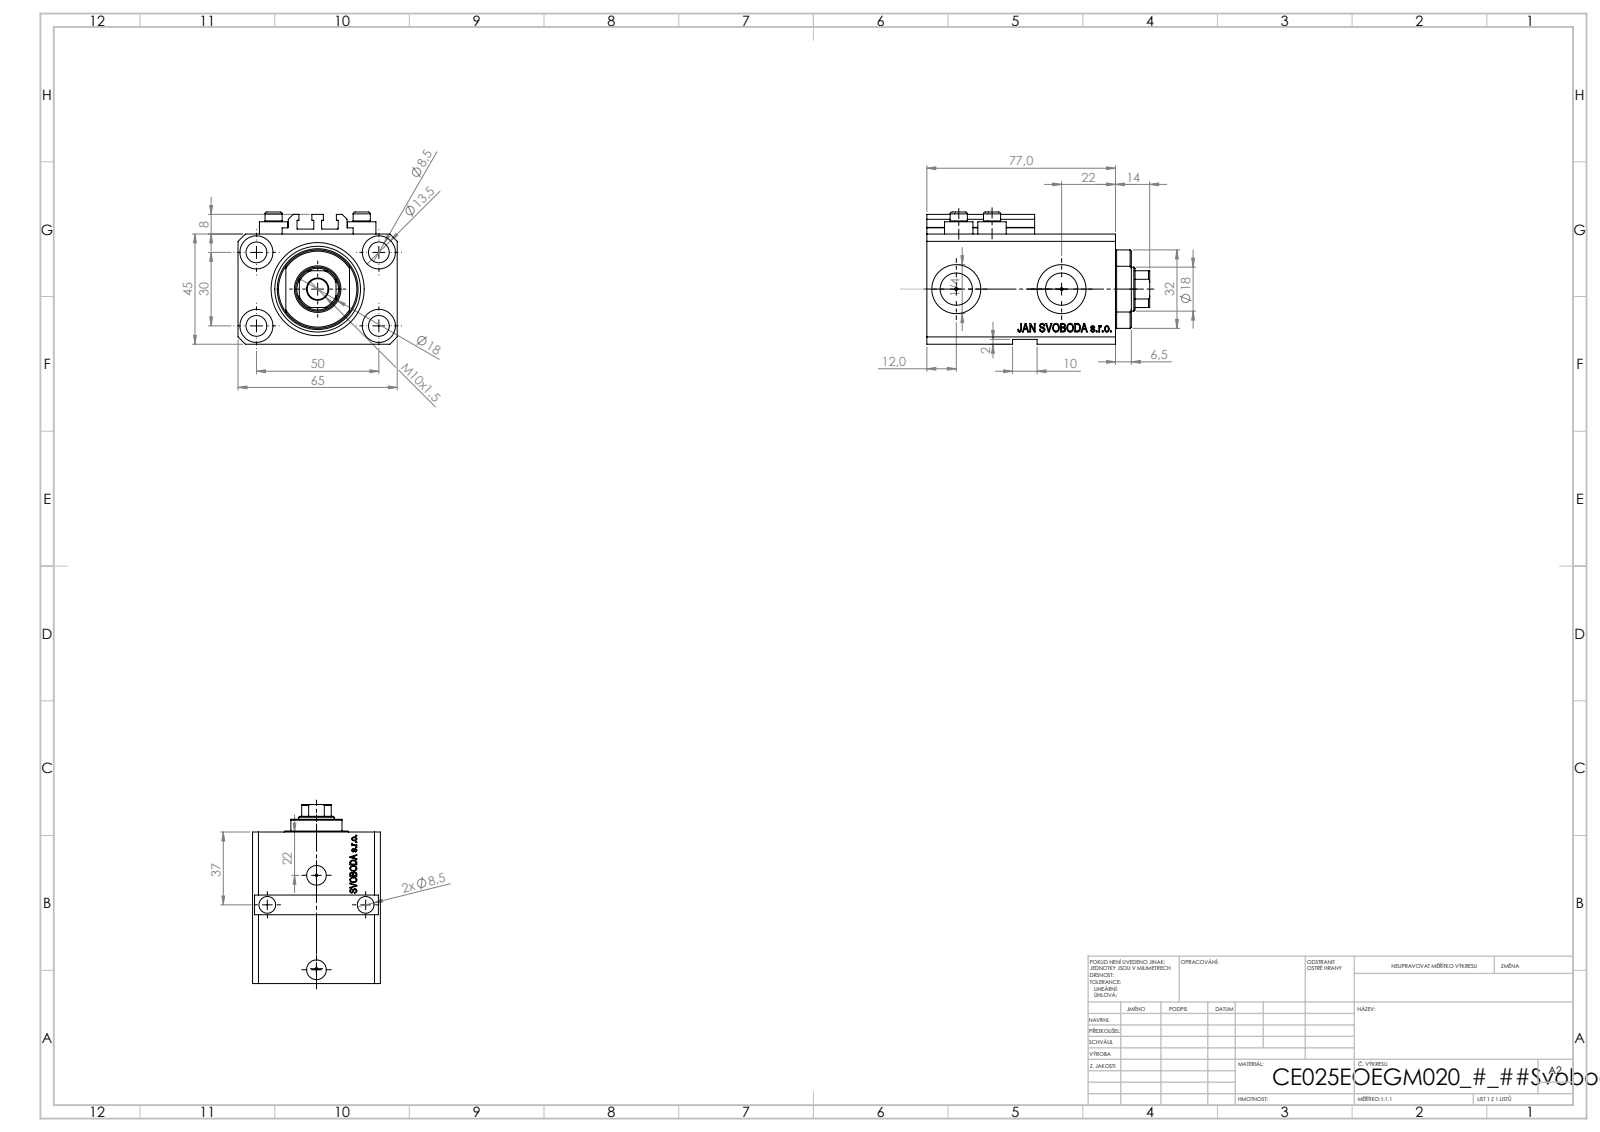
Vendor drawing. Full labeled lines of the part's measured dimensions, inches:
Part name (STEP PRODUCT): V250CE_C_VCP; V250CE_VC_E; V250CE_E_Body; ALLEN BOLT V250CE
STEP written by: SolidWorks 2019 (CONFIG_CONTROL_DESIGN)
Units: inches
Bodies: 8 solids, 1067 faces (511 planar, 126 cylindrical, 430 other)
Overall size (bounding box): 3.583 × 2.559 × 2.126
Volume: 12.19 in³ · Surface area: 91.74 in²
Round holes (diameter × count): ⌀0.335 ×7, ⌀0.049 ×4, ⌀0.157 ×4, ⌀0.531 ×4, ⌀0.394 ×2, ⌀0.518 ×2, ⌀0.787 ×2, ⌀0.709 ×1, ⌀0.984 ×1, ⌀1.496 ×1
Round bosses / shafts (diameter × count): ⌀0.457 ×4, ⌀0.276 ×4
Partial cylindrical surfaces — rounded edges, fillets, slot ends (radius × count): R0.008 ×10, R0.335 ×1, R0.63 ×1
Main face-to-face distances: 1.772, 2.559, 2.48, 0.551, 3.031, 0.079, 0.272, 2.209, 2.76, 1.85
Hole centre spacings: 1.148, 1.969, 0.535, 0.595, 0.741, 0.747, 1.032, 1.048
